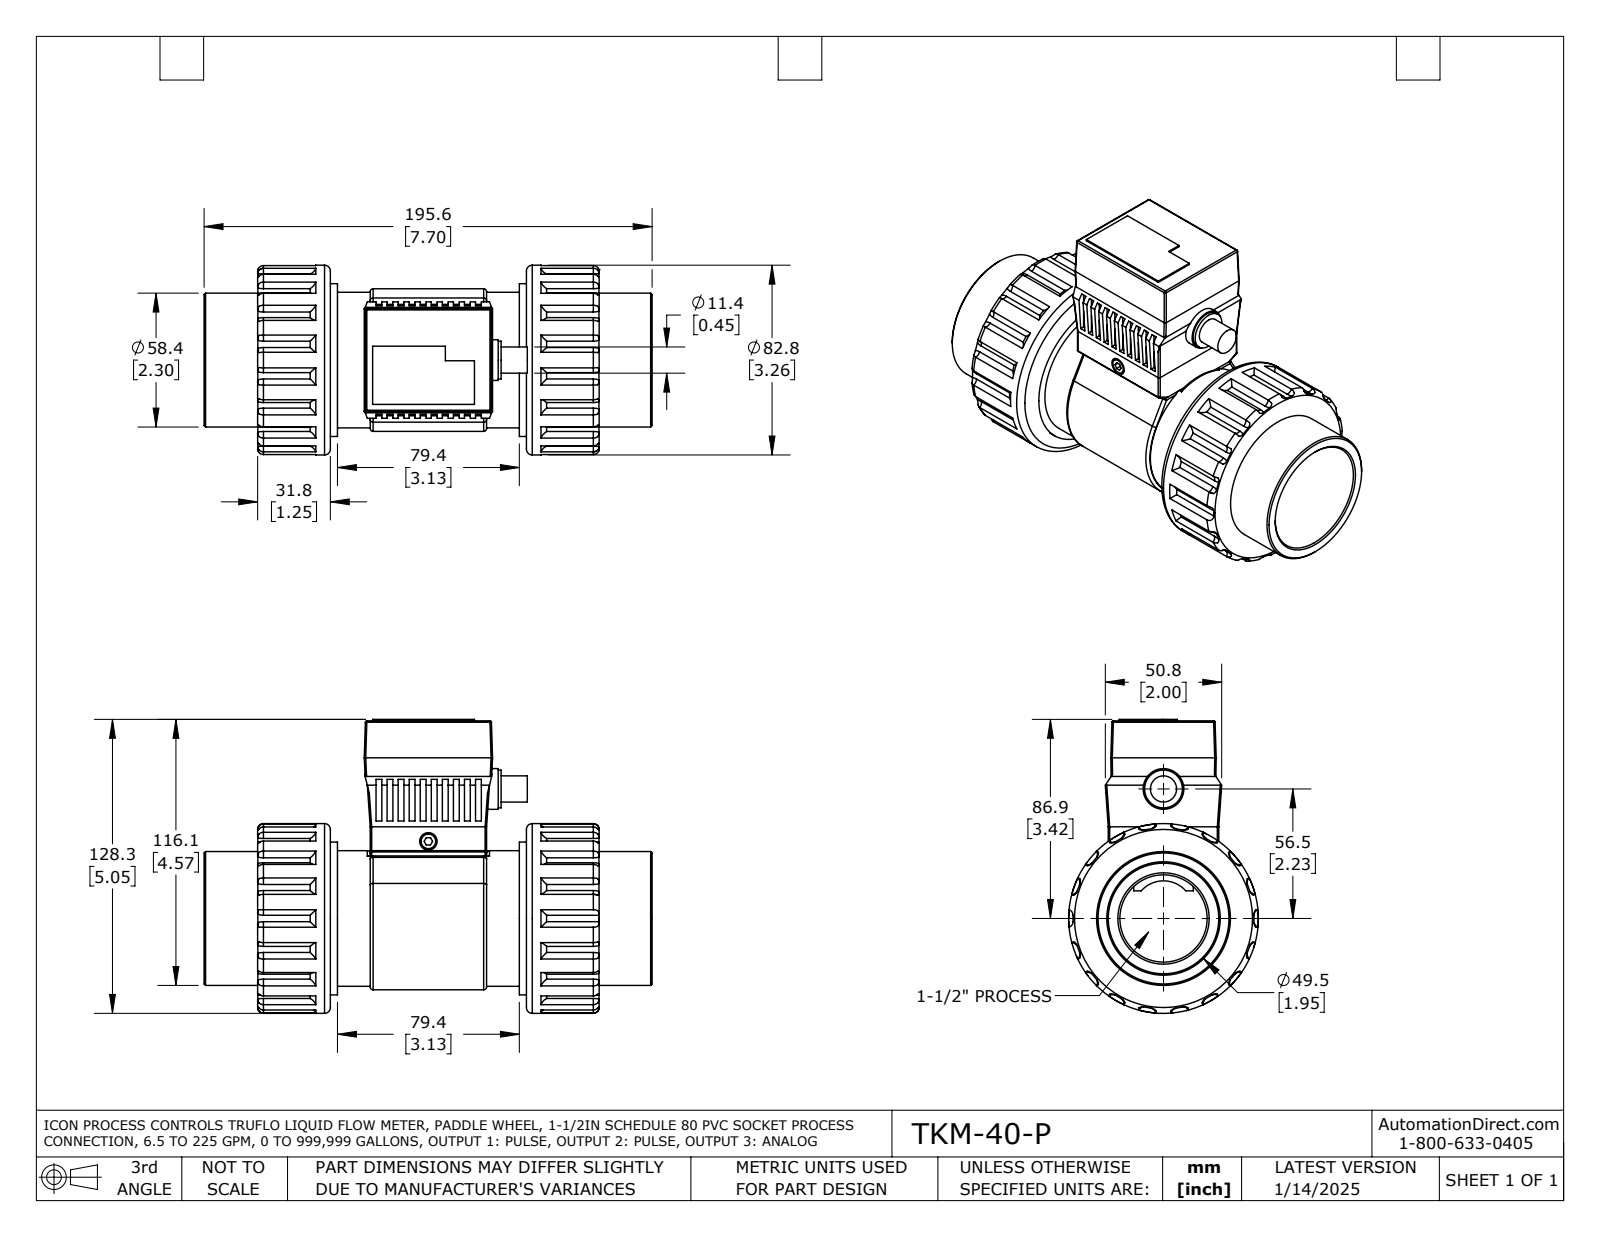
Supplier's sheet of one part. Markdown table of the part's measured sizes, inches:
| quantity | value |
| --- | --- |
| part name | TKM-40-P |
| STEP written by | SolidWorks 2021 (AUTOMOTIVE_DESIGN) |
| units | inches |
| bodies | 9 solids, 624 faces (233 planar, 207 cylindrical, 184 other) |
| overall size | 7.7 × 5.05 × 3.26 |
| volume | 36.45 in³ |
| surface area | 223.3 in² |
| round holes (diameter × count) | 0.128 × 4, 0.3 × 1, 1.1 × 1, 1.2 × 1, 1.5 × 1, 1.57 × 1, 1.9 × 1, 2.2 × 1, 2.3 × 1, 2.445 × 1 |
| round bosses / shafts (diameter × count) | 3.26 × 1, 2.625 × 1, 2.48 × 1, 2.33 × 1, 1.933 × 1, 1.024 × 1, 0.7 × 1, 0.65 × 1 |
| partial cylindrical surfaces (radius × count) | 0.1 × 36, 0.025 × 26, 0.05 × 10, 0.465 × 1, 0.512 × 1, 1.225 × 1 |
| main face-to-face distances | 1.25, 5.285, 0.585, 4.62, 0.665, 4.035, 0.685, 3.935, 4.7, 0.1 |
| hole center spacings | 0.979, 1.181, 1.561, 1.957 |
